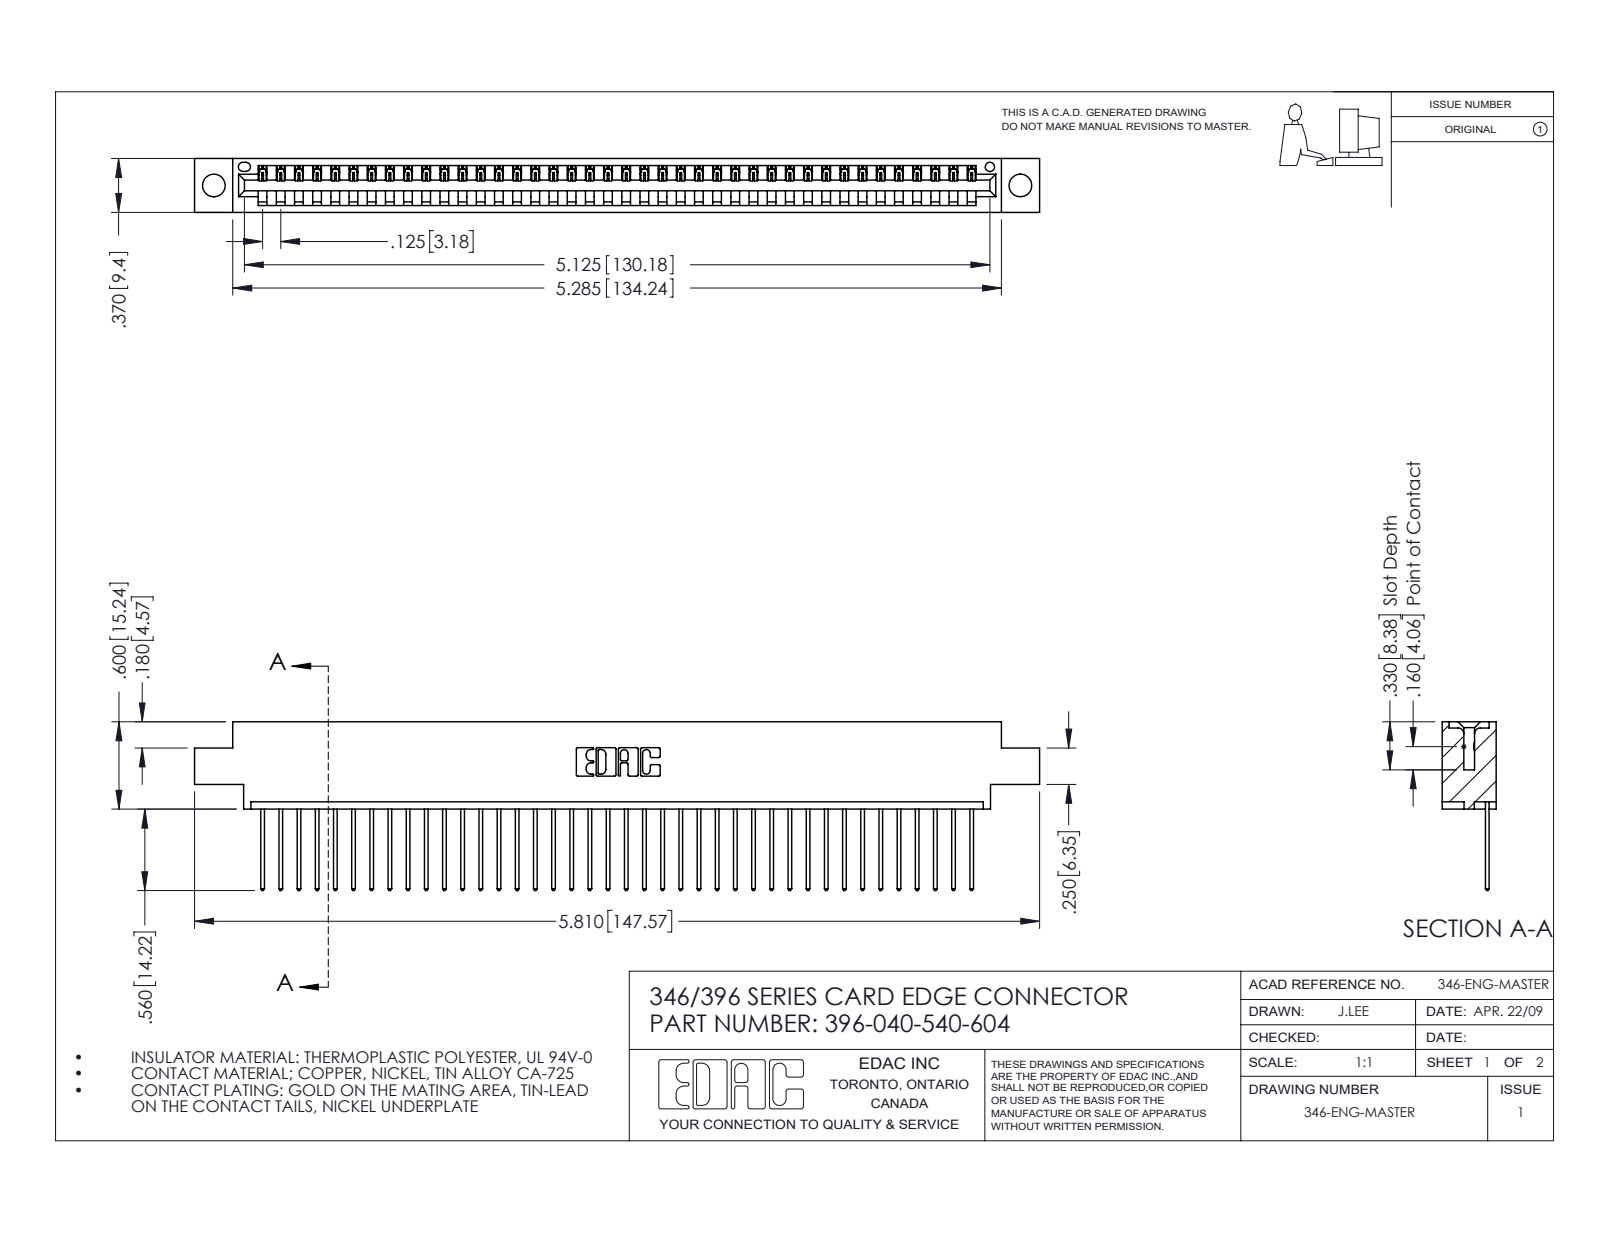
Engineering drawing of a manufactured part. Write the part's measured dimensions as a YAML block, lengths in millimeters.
part_name: "346 Part_0.170 Offset - 0.156 Dia-TH; 396-040-540-604; 345-292-001_345-293-140"
step_written_by: "SolidWorks 2016 (CONFIG_CONTROL_DESIGN)"
units: millimeters
bodies: {solids: 41, faces: 2446, planar: 1680, cylindrical: 766, other: 0}
overall_size: [147.6, 29.5, 9.4]
volume: 13900
surface_area: 17740
round_holes:
  - {diameter: 4, count: 2}
  - {diameter: 1.6, count: 1}
partial_cylinders:
  - {radius: 0.2, count: 80}
  - {radius: 0.3, count: 80}
  - {radius: 0.3, count: 22}
  - {radius: 0.2, count: 6}
  - {radius: 0.8, count: 6}
  - {radius: 0.7, count: 3}
  - {radius: 0.8, count: 2}
  - {radius: 1, count: 2}
face_to_face_distances: [1.2, 8.2, 9.4, 6.4, 1.8, 7.6, 0.6, 3.8, 5.6, 2.5]
hole_center_spacings: [6.2, 135.5, 140.8]
